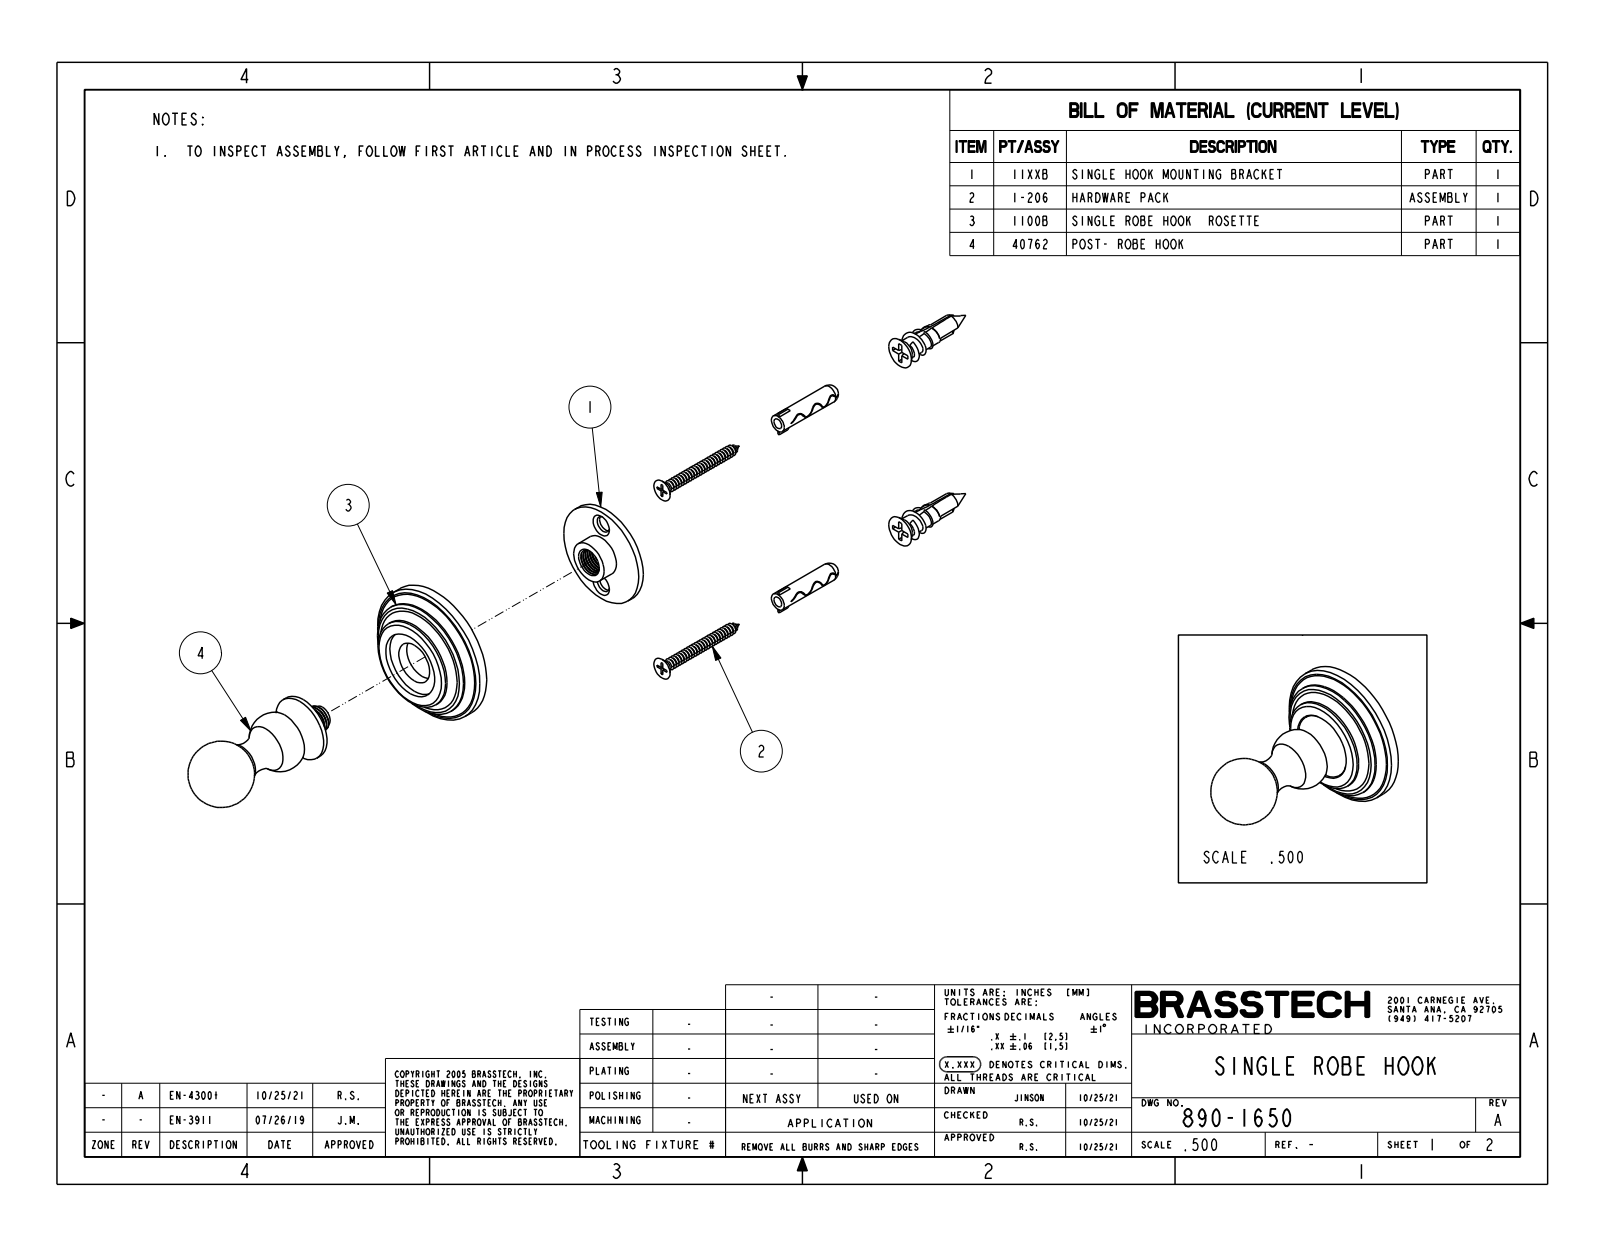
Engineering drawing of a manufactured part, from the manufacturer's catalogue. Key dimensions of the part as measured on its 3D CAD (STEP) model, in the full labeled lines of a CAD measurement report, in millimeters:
Part name (STEP PRODUCT): 890-1650
STEP written by: CREO PARAMETRIC BY PTC INC, 2018400 (CONFIG_CONTROL_DESIGN)
Units: millimetres
Bodies: 1 solid, 30 faces (4 planar, 8 cylindrical, 18 other)
Overall size (bounding box): 62.7 × 50 × 50
Volume: 31 090 mm³ · Surface area: 7 955 mm²
Round bosses / shafts (diameter × count): ⌀50 ×1, ⌀42 ×1, ⌀32.8 ×1, ⌀13.6 ×1
Main face-to-face distances: 12.7, 8.4, 4.3, 4.4, 4.1, 8.3
